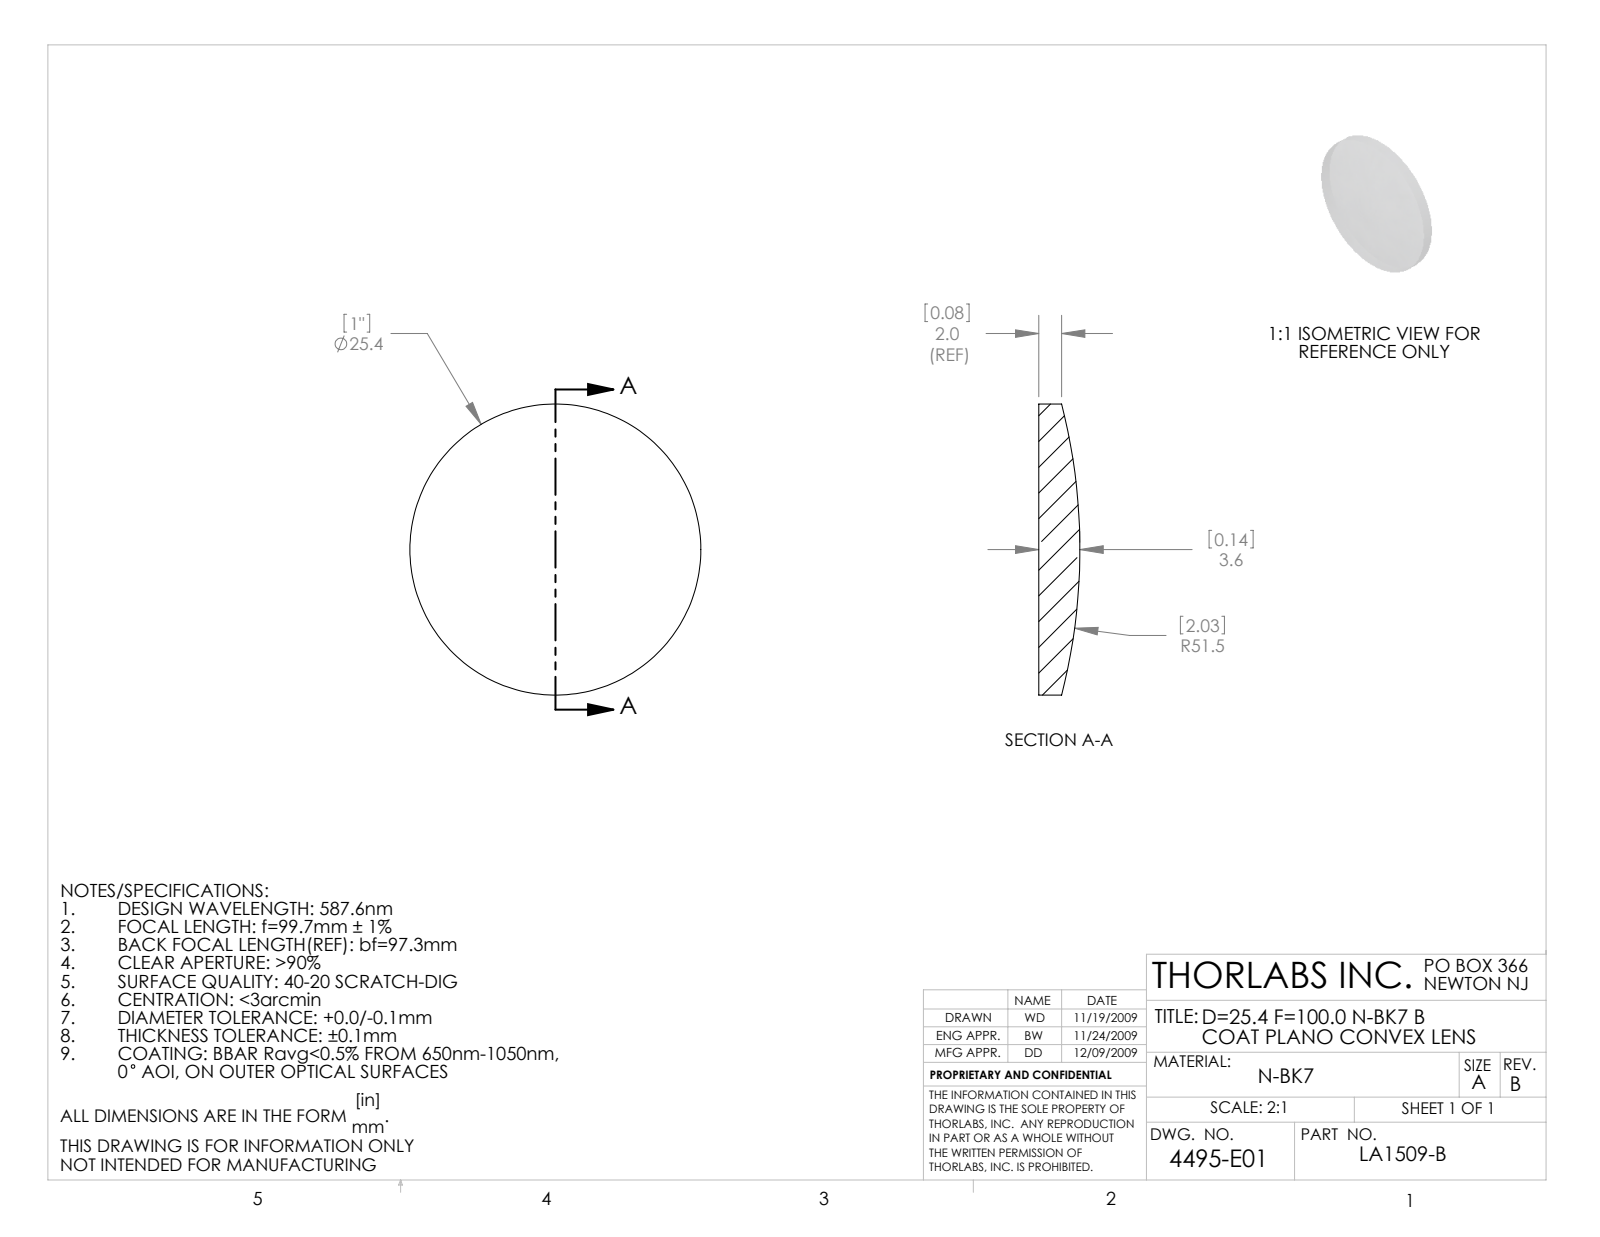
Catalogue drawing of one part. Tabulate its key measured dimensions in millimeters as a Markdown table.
| quantity | value |
| --- | --- |
| part name | 4495-E0W |
| STEP written by | SolidWorks 2009 (AUTOMOTIVE_DESIGN) |
| units | millimeters |
| bodies | 1 solid, 5 faces (1 planar, 2 cylindrical, 2 other) |
| overall size | 25.4 × 25.4 × 3.59 |
| volume | 1 418 mm³ |
| surface area | 1 181 mm² |
| round bosses / shafts (diameter × count) | 25.4 × 1 |
